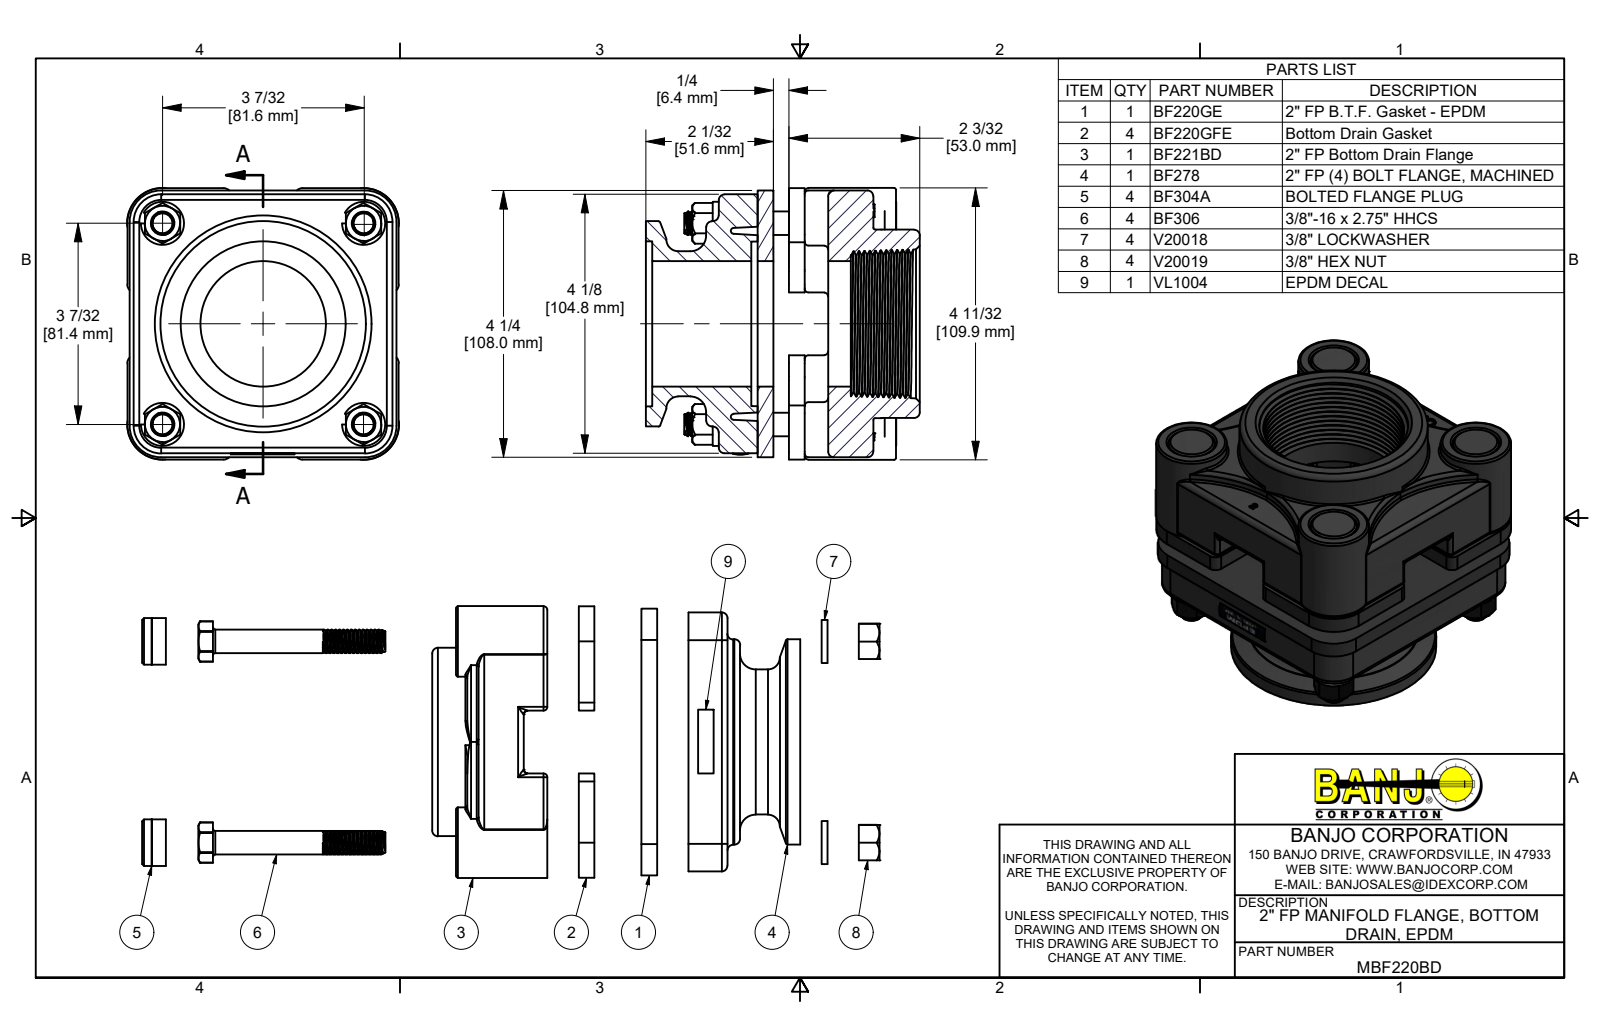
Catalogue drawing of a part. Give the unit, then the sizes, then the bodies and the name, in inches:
Units: inches
Overall size (bounding box): 38.212 × 4.328 × 4.328
Round holes (diameter × count): ⌀0.307 ×4, ⌀0.375 ×4, ⌀0.38 ×4, ⌀0.385 ×4, ⌀0.41 ×4, ⌀0.438 ×4, ⌀0.72 ×4, ⌀0.745 ×4, ⌀2 ×1, ⌀2.62 ×1, ⌀2.63 ×1, ⌀3 ×1
Round bosses / shafts (diameter × count): ⌀0.324 ×60, ⌀1.125 ×4, ⌀0.742 ×4, ⌀0.687 ×4, ⌀0.375 ×4, ⌀3.27 ×1, ⌀2.31 ×1
Partial cylindrical surfaces — rounded edges, fillets, slot ends (radius × count): R0.06 ×44, R0.125 ×24, R0.09 ×12, R0.03 ×8, R0.162 ×8, R2 ×8, R0.32 ×4, R0.44 ×4
Main face-to-face distances: 0.25, 0.5, 0.25, 0.75, 0.062, 4.187, 0.75, 0.5, 0.25, 0.375
Hole centre spacings: 3.204, 2.265, 2.265, 3.203, 3.204, 4.53, 4.53, 4.531
Volume: 34.88 in³ · Surface area: 525.8 in²
Bodies: 24 solids, 1275 faces (337 planar, 431 cylindrical, 507 other)
Part name (STEP PRODUCT): MBF220BD; BF221BD; BF278; V25378X (+7 more)
STEP written by: Autodesk Inventor 2019 (AUTOMOTIVE_DESIGN)
